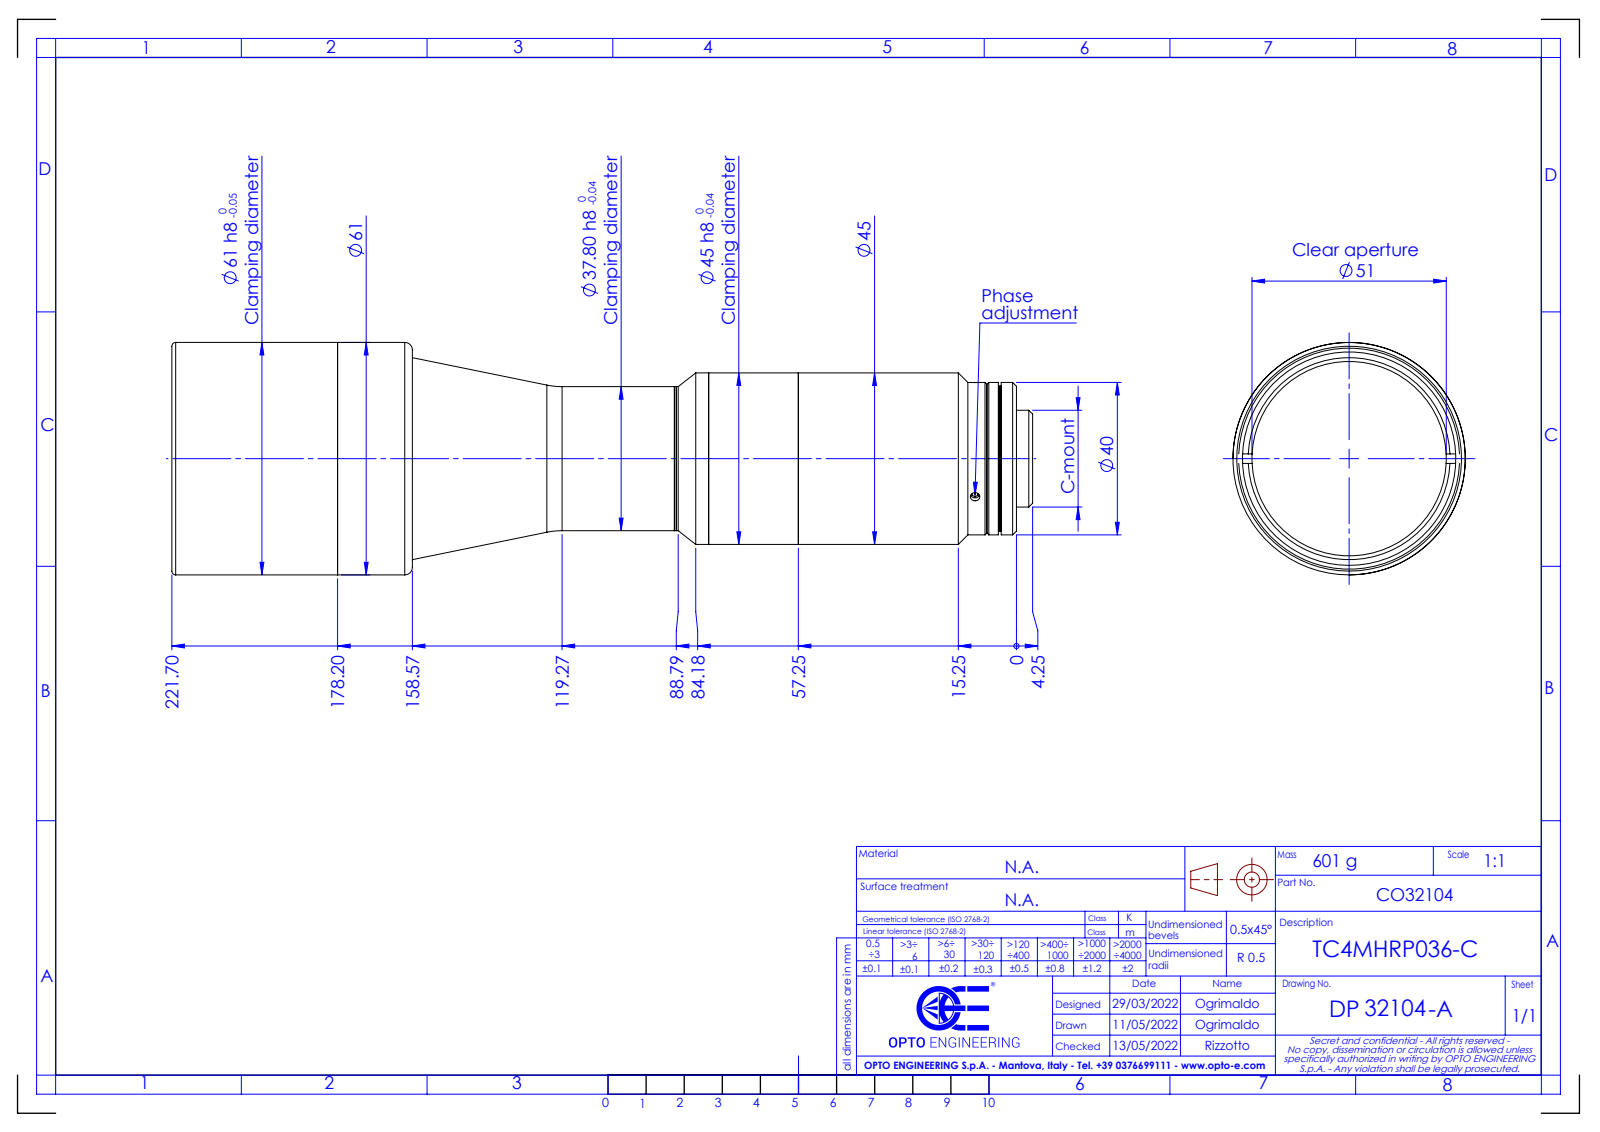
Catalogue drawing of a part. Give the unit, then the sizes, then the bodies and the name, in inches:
Units: inches
Overall size (bounding box): 8.895 × 2.402 × 2.402
Round holes (diameter × count): ⌀0.098 ×3, ⌀0.886 ×1, ⌀2.008 ×1, ⌀2.087 ×1, ⌀2.205 ×1
Round bosses / shafts (diameter × count): ⌀2.402 ×1, ⌀1.772 ×1, ⌀1.575 ×1, ⌀1.496 ×1, ⌀1.488 ×1, ⌀1 ×1
Main face-to-face distances: 3.358, 3.328, 0.03, 3.515, 0.187, 0.157, 3.5, 6.829, 6.858, 7.016
Bodies: 0 solids, 97 faces (31 planar, 42 cylindrical, 24 other)
Part name (STEP PRODUCT): DP32104-A_TC4MHRP036-C
STEP written by: SolidWorks 2021 (CONFIG_CONTROL_DESIGN)
